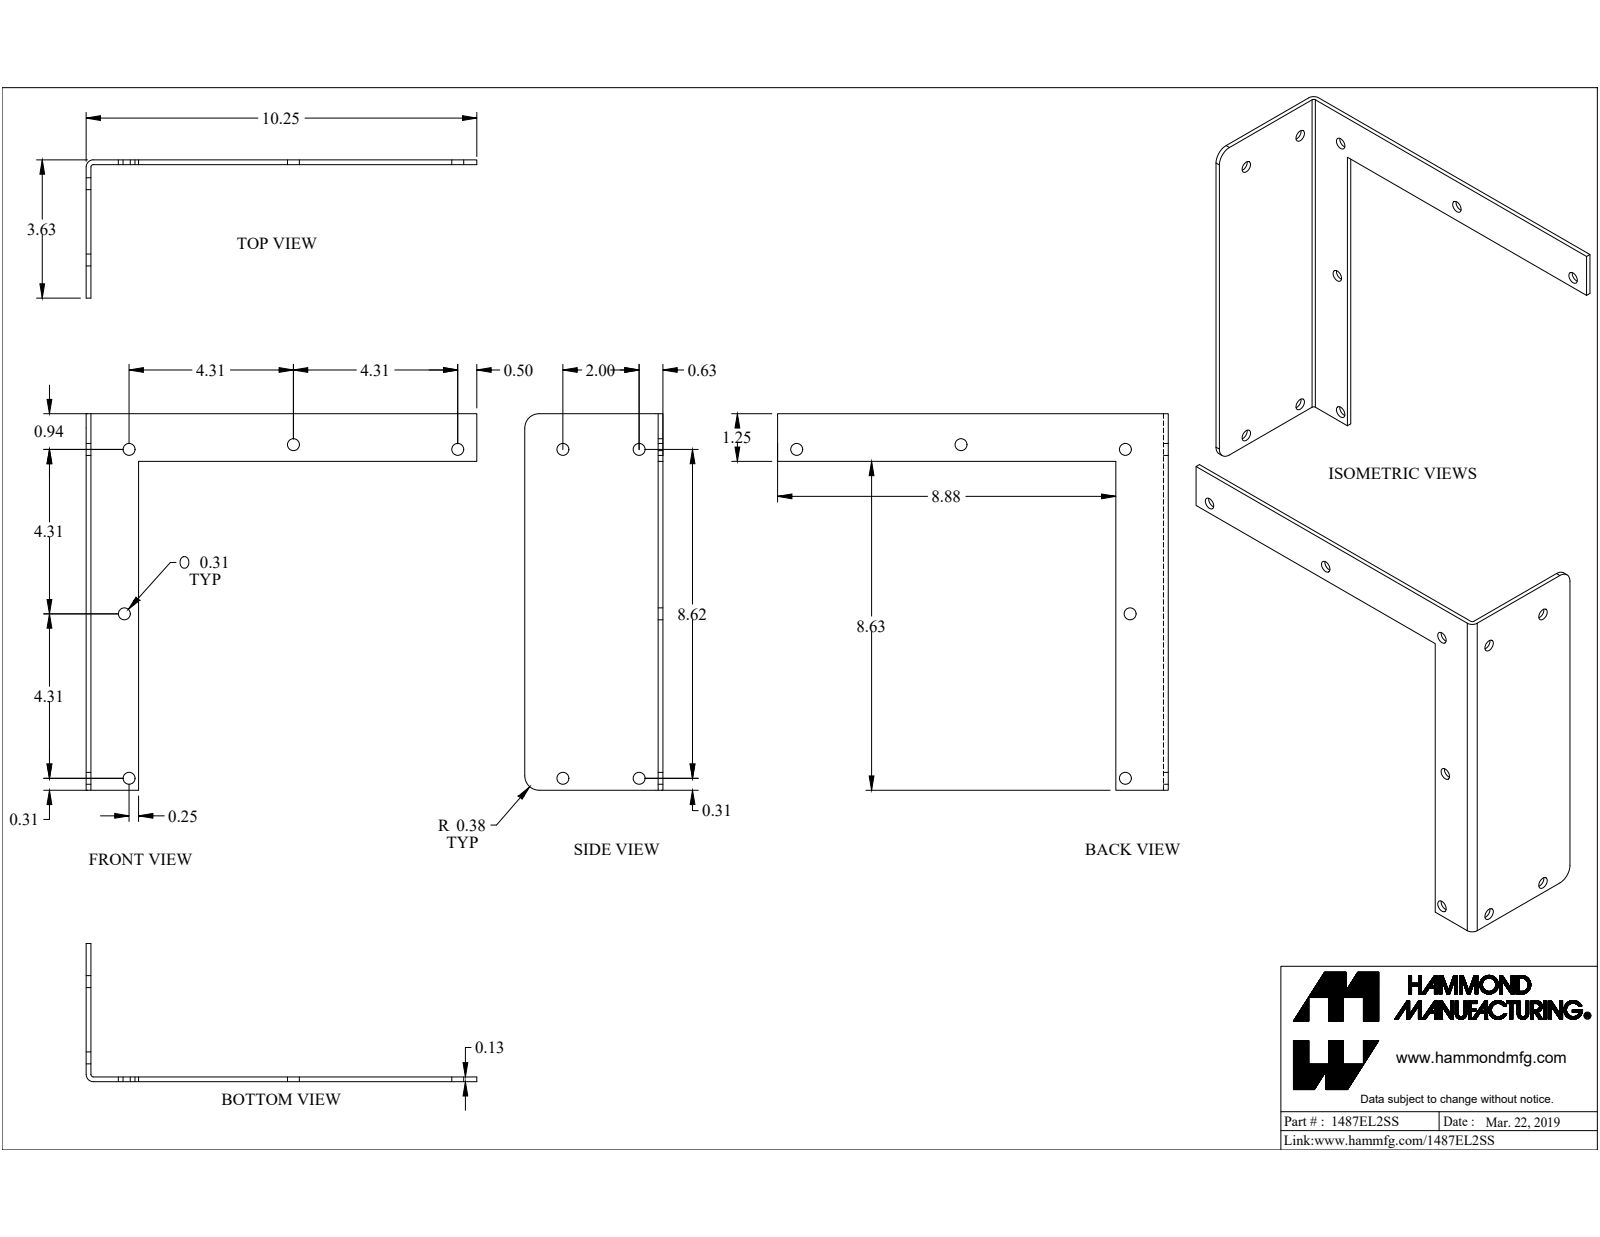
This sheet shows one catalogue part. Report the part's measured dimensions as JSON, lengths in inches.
{"part_name": "1487EL2SS", "step_written_by": "SolidWorks 2019 (CONFIG_CONTROL_DESIGN)", "units": "inches", "bodies": {"solids": 6, "faces": 228, "planar": 144, "cylindrical": 49, "other": 35}, "overall_size": [12.25, 10.125, 4.875], "volume_in3": 7.746, "surface_area_in2": 147.5, "round_holes": [[0.313, 9], [0.196, 1], [0.258, 1], [0.35, 1]], "round_bosses_or_shafts": [[0.5, 1], [0.25, 1]], "partial_cylinders_radius": [[0.02, 6], [0.375, 6], [0.06, 1], [0.185, 1], [0.25, 1]], "face_to_face_distances": [0.125, 0.03, 9.845, 9.875, 1.25, 1.375, 3.5, 3.625, 1.25, 8.595], "hole_center_spacings": [8.624, 2, 8.853, 0.699, 1.168, 2.643, 4.313, 4.314]}
